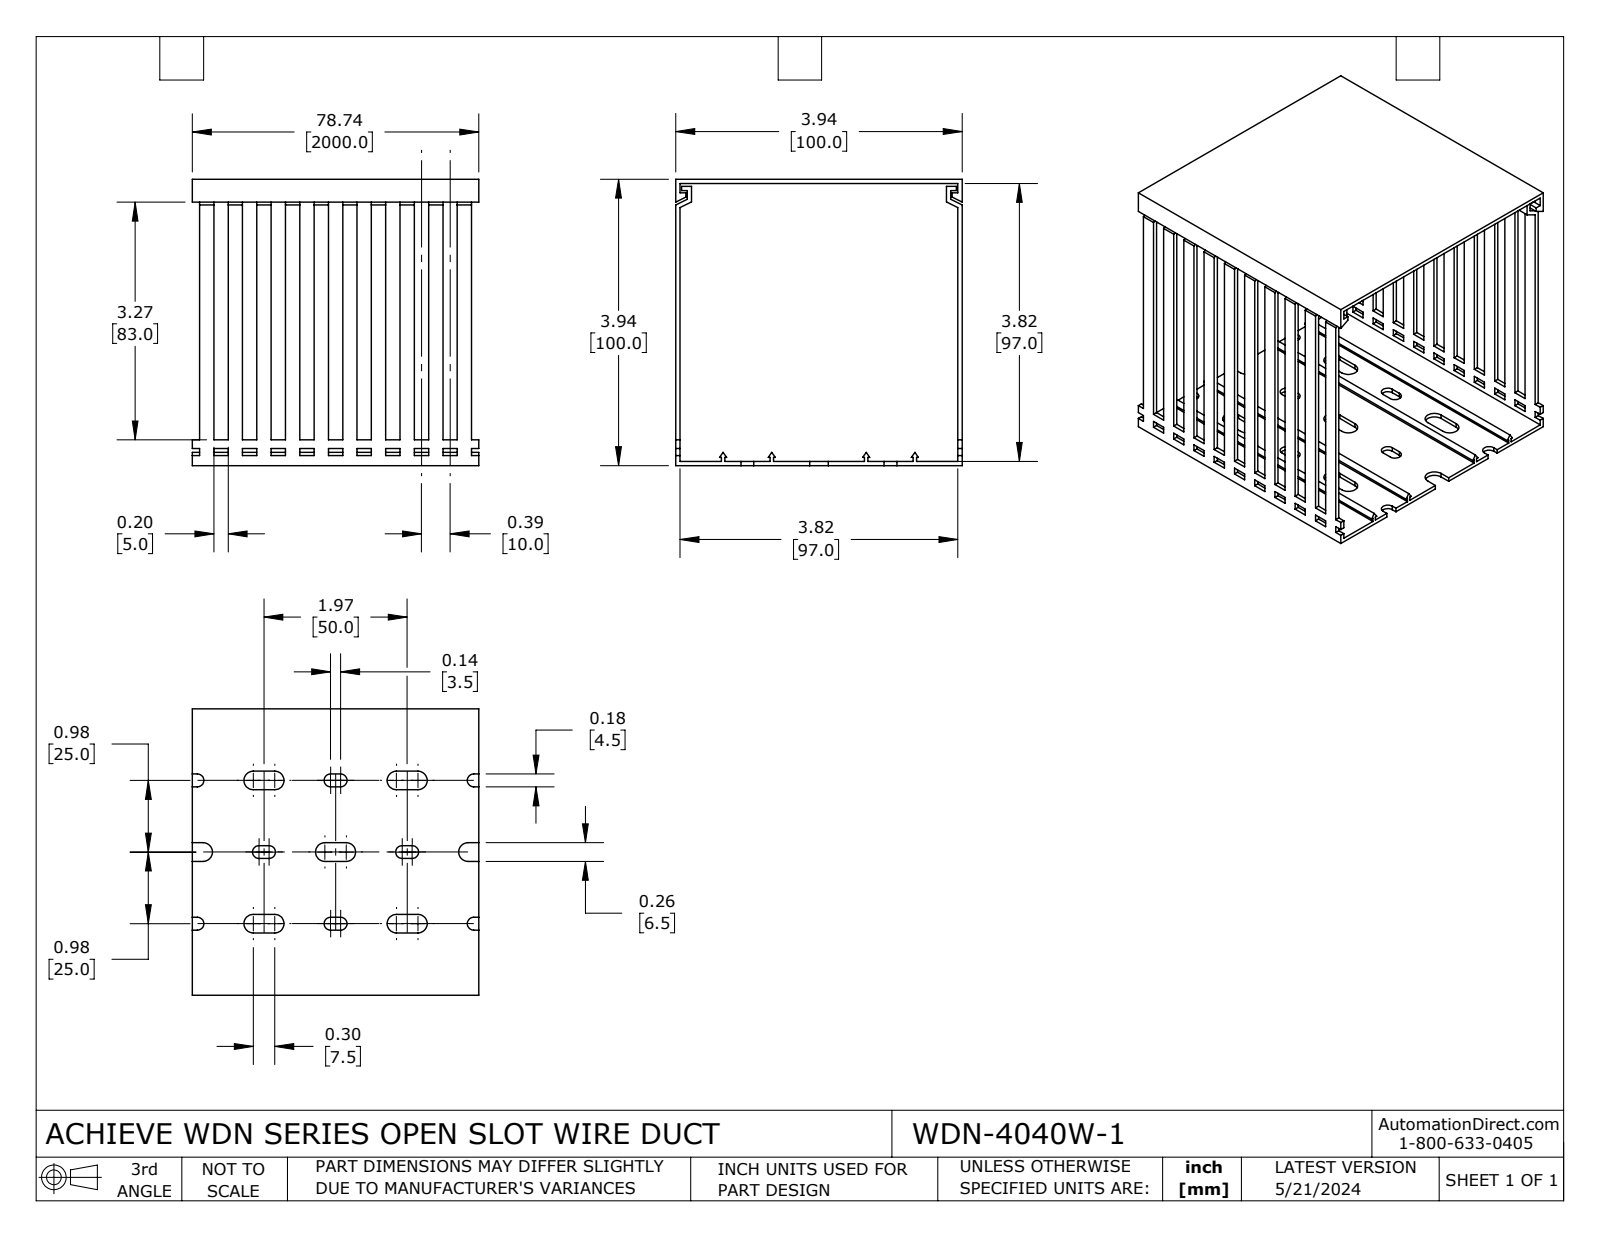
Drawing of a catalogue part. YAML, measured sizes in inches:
part_name: "WDN-4040W-1"
step_written_by: "SolidWorks 2023 (CONFIG_CONTROL_DESIGN)"
units: inches
bodies: {solids: 2, faces: 412, planar: 376, cylindrical: 36, other: 0}
overall_size: [3.937, 3.937, 3.937]
volume: 2.989
surface_area: 114
partial_cylinders:
  - {radius: 0.089, count: 12}
  - {radius: 0.128, count: 12}
face_to_face_distances: [0.059, 3.878, 3.937, 3.819, 0.394, 0.197, 0.591, 0.787, 0.984, 1.181]
